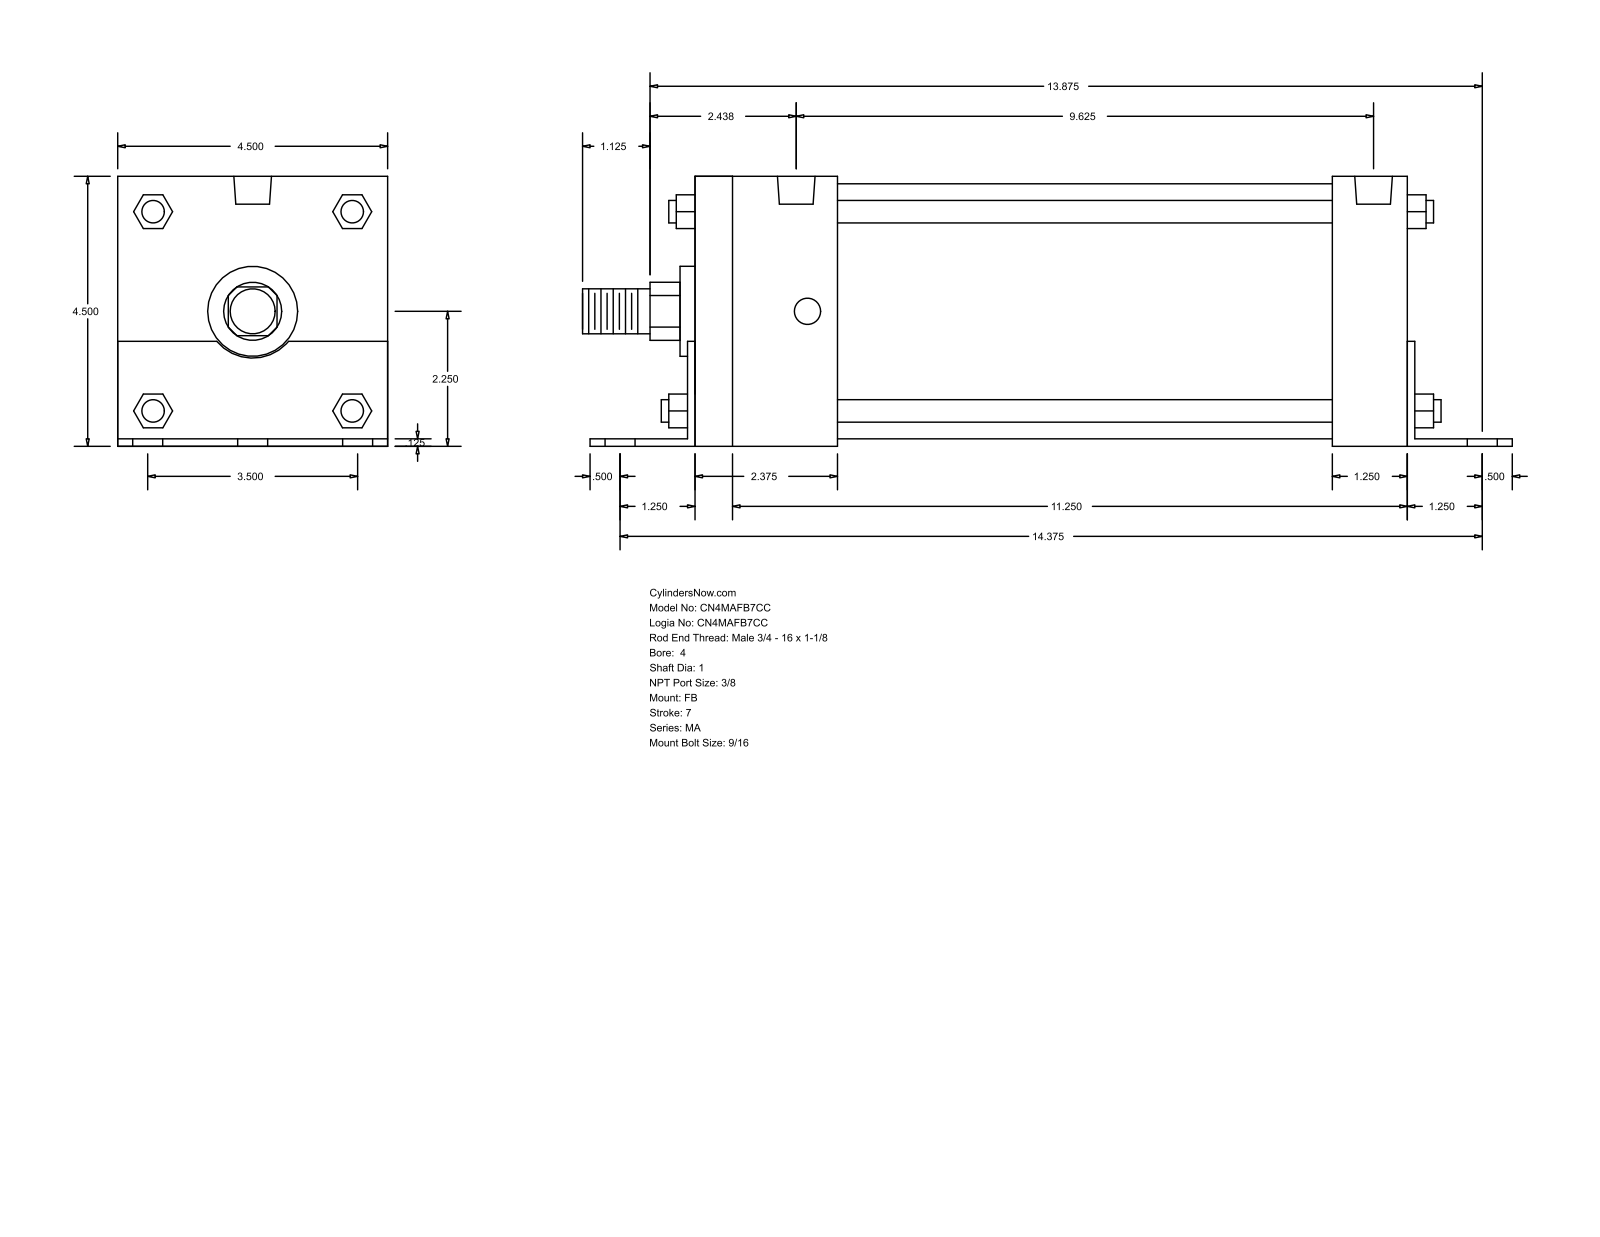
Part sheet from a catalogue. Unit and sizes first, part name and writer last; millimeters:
Units: millimetres
Overall size (bounding box): 393.7 × 114.35 × 114.3
Round holes (diameter × count): ⌀14.29 ×6, ⌀11.11 ×4, ⌀15.93 ×2
Round bosses / shafts (diameter × count): ⌀9.53 ×4, ⌀107.95 ×1, ⌀38.1 ×1, ⌀25.4 ×1, ⌀19.05 ×1
Partial cylindrical surfaces — rounded edges, fillets, slot ends (radius × count): R12.29 ×1, R19.81 ×1
Main face-to-face distances: 114.3, 3.17, 114.35, 304.8, 3.12, 111.18, 301.63, 307.97, 273.05, 269.88
Hole centre spacings: 44.45, 367.83, 365.13, 64, 67.51, 86.85, 88.9, 90.97
Bodies: 0 solids, 140 faces (105 planar, 35 cylindrical, 0 other)
Part name (STEP PRODUCT): MA_FB__0400_1
STEP written by: GSSL Pune (CONFIG_CONTROL_DESIGN)
